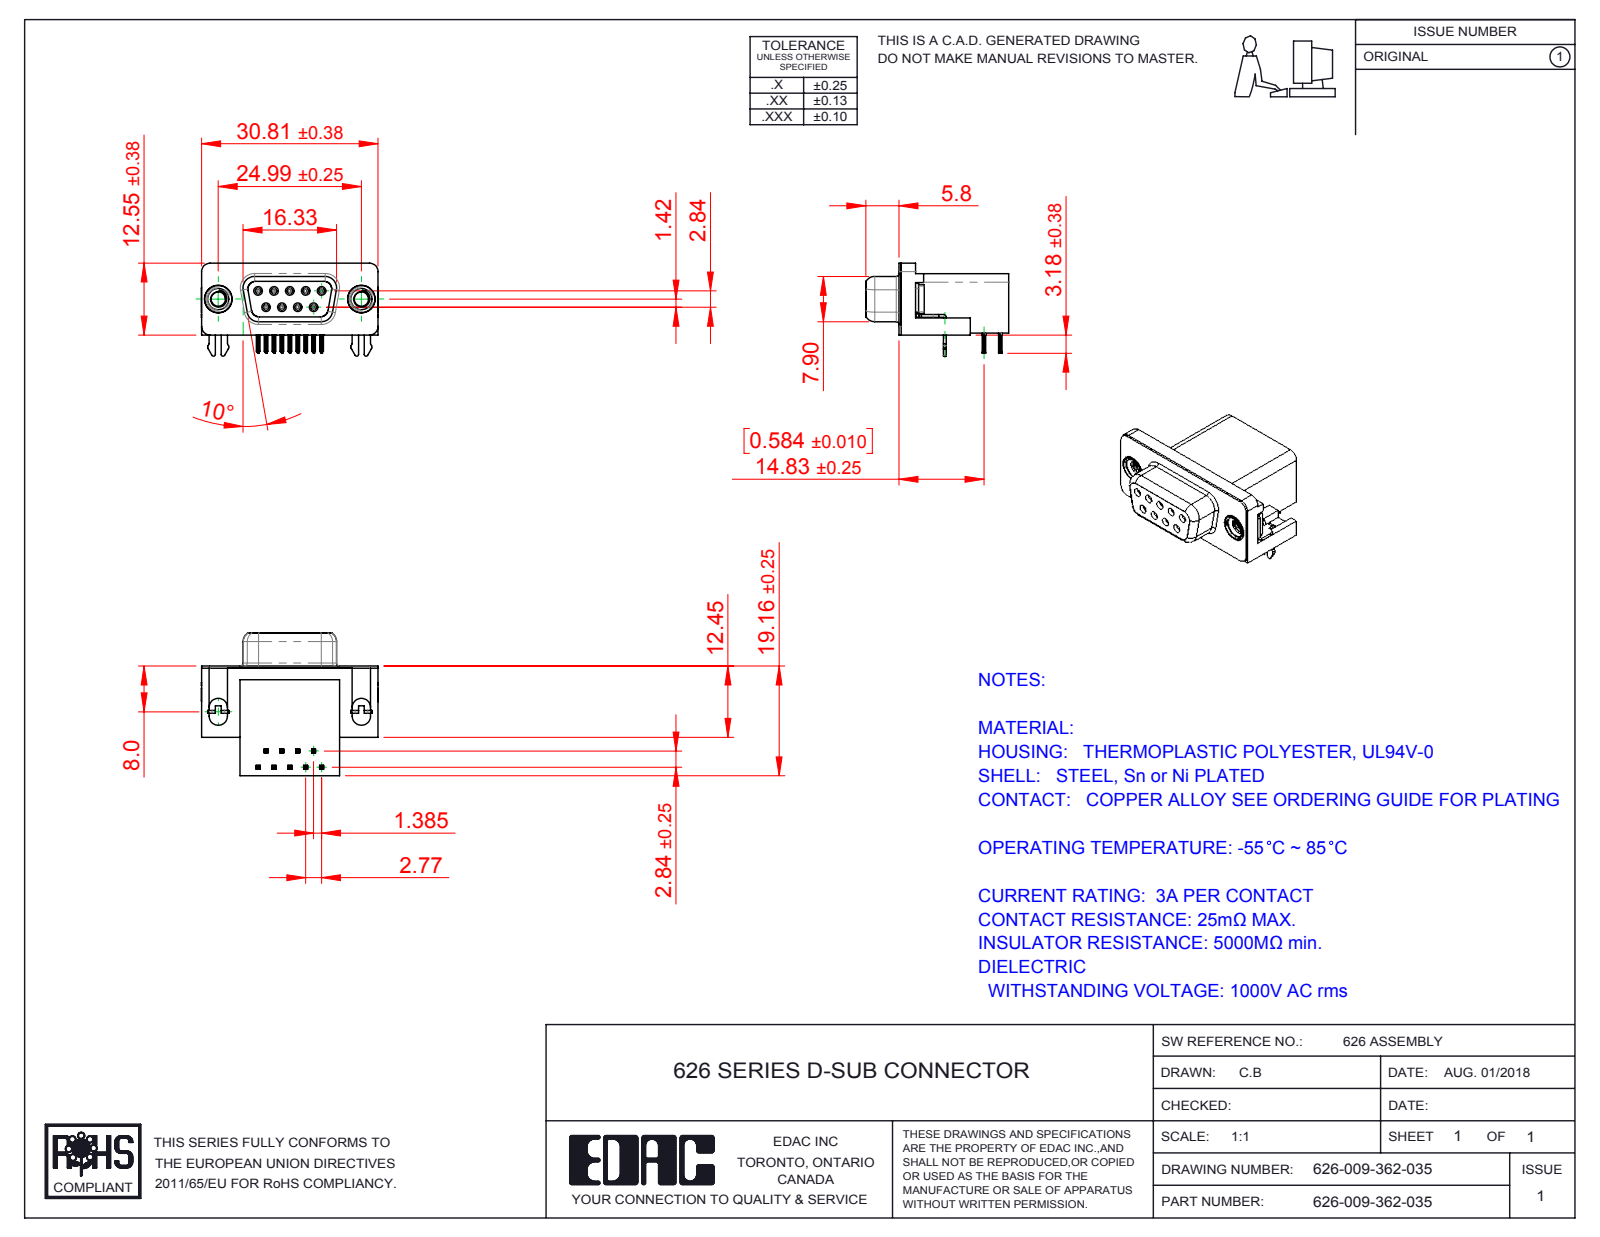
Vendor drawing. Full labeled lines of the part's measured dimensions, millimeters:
Part name (STEP PRODUCT): 626 Housing_9 Socket; 626-009-362-035; 626 Contact Bottom; 626 Shell_9 Socket (+3 more)
STEP written by: SolidWorks 2016 (CONFIG_CONTROL_DESIGN)
Units: millimetres
Bodies: 15 solids, 1612 faces (716 planar, 428 cylindrical, 468 other)
Overall size (bounding box): 30.89 × 24.96 × 16.25
Volume: 4 962 mm³ · Surface area: 5 800 mm²
Round holes (diameter × count): ⌀0.8 ×9, ⌀0.9 ×9, ⌀2.5 ×2, ⌀4 ×2, ⌀4.8 ×2, ⌀5 ×2
Round bosses / shafts (diameter × count): ⌀1.2 ×9, ⌀4.9 ×2, ⌀4.75 ×2, ⌀3.9 ×2
Partial cylindrical surfaces — rounded edges, fillets, slot ends (radius × count): R0.1 ×72, R0.15 ×36, R0.35 ×18, R1 ×18, R0.5 ×10, R0.34 ×9, R0.25 ×8, R1.35 ×8
Main face-to-face distances: 0.4, 10.34, 0.35, 18.76, 19.16, 2.9, 2.5, 6.2, 16.26, 0.5
Hole centre spacings: 3.16, 2.77, 5.54, 5.03, 5.04, 8.31, 7.48, 7.49
